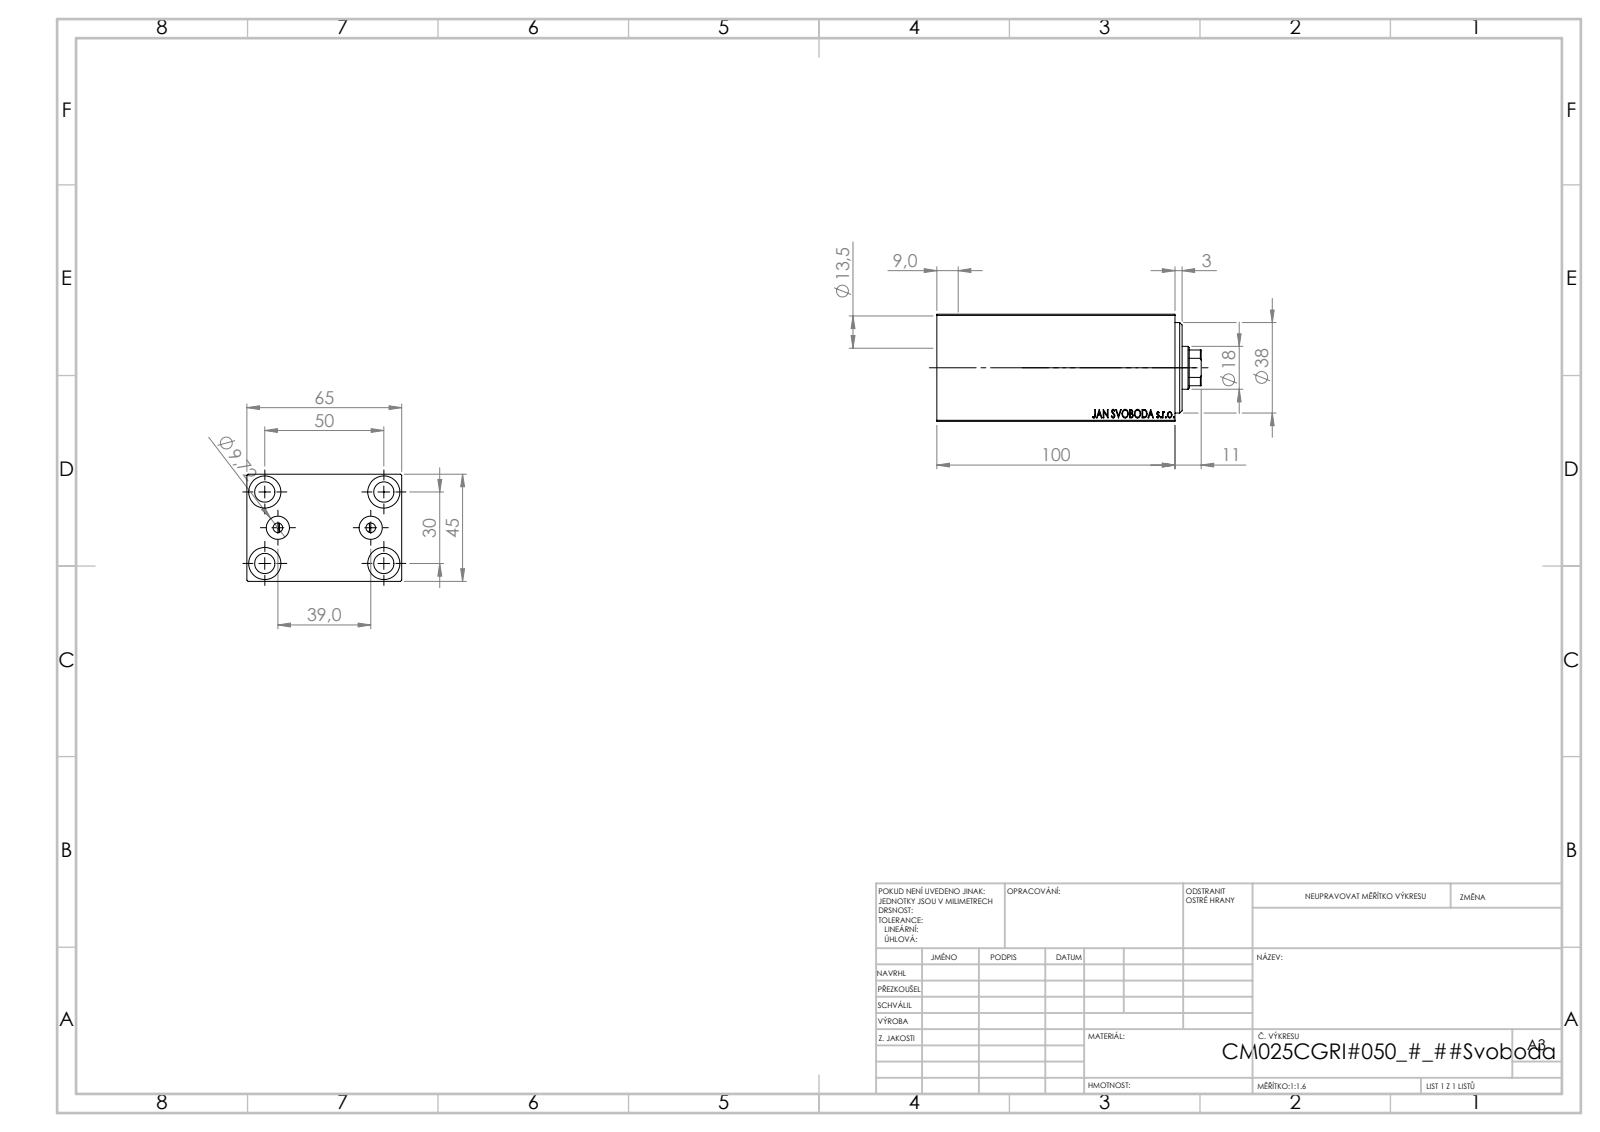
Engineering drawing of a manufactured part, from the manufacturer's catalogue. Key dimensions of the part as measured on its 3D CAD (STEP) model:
Part name (STEP PRODUCT): V450CM_VC_B; V450CM_C_VCP; V450CM_C_Body
STEP written by: SolidWorks 2019 (CONFIG_CONTROL_DESIGN)
Units: millimetres
Bodies: 3 solids, 858 faces (408 planar, 56 cylindrical, 394 other)
Overall size (bounding box): 111 × 65 × 45
Volume: 252 071 mm³ · Surface area: 61 495 mm²
Round holes (diameter × count): ⌀8.5 ×5, ⌀13.5 ×4, ⌀4 ×2, ⌀9.72 ×2, ⌀18 ×1, ⌀21.5 ×1, ⌀25 ×1, ⌀27 ×1, ⌀38 ×1
Partial cylindrical surfaces — rounded edges, fillets, slot ends (radius × count): R8.5 ×1
Main face-to-face distances: 45, 65, 6, 89, 94, 95, 5, 100, 3, 8
Hole centre spacings: 15.98, 29.15, 46.96, 19.5, 30, 50, 58.31, 39
